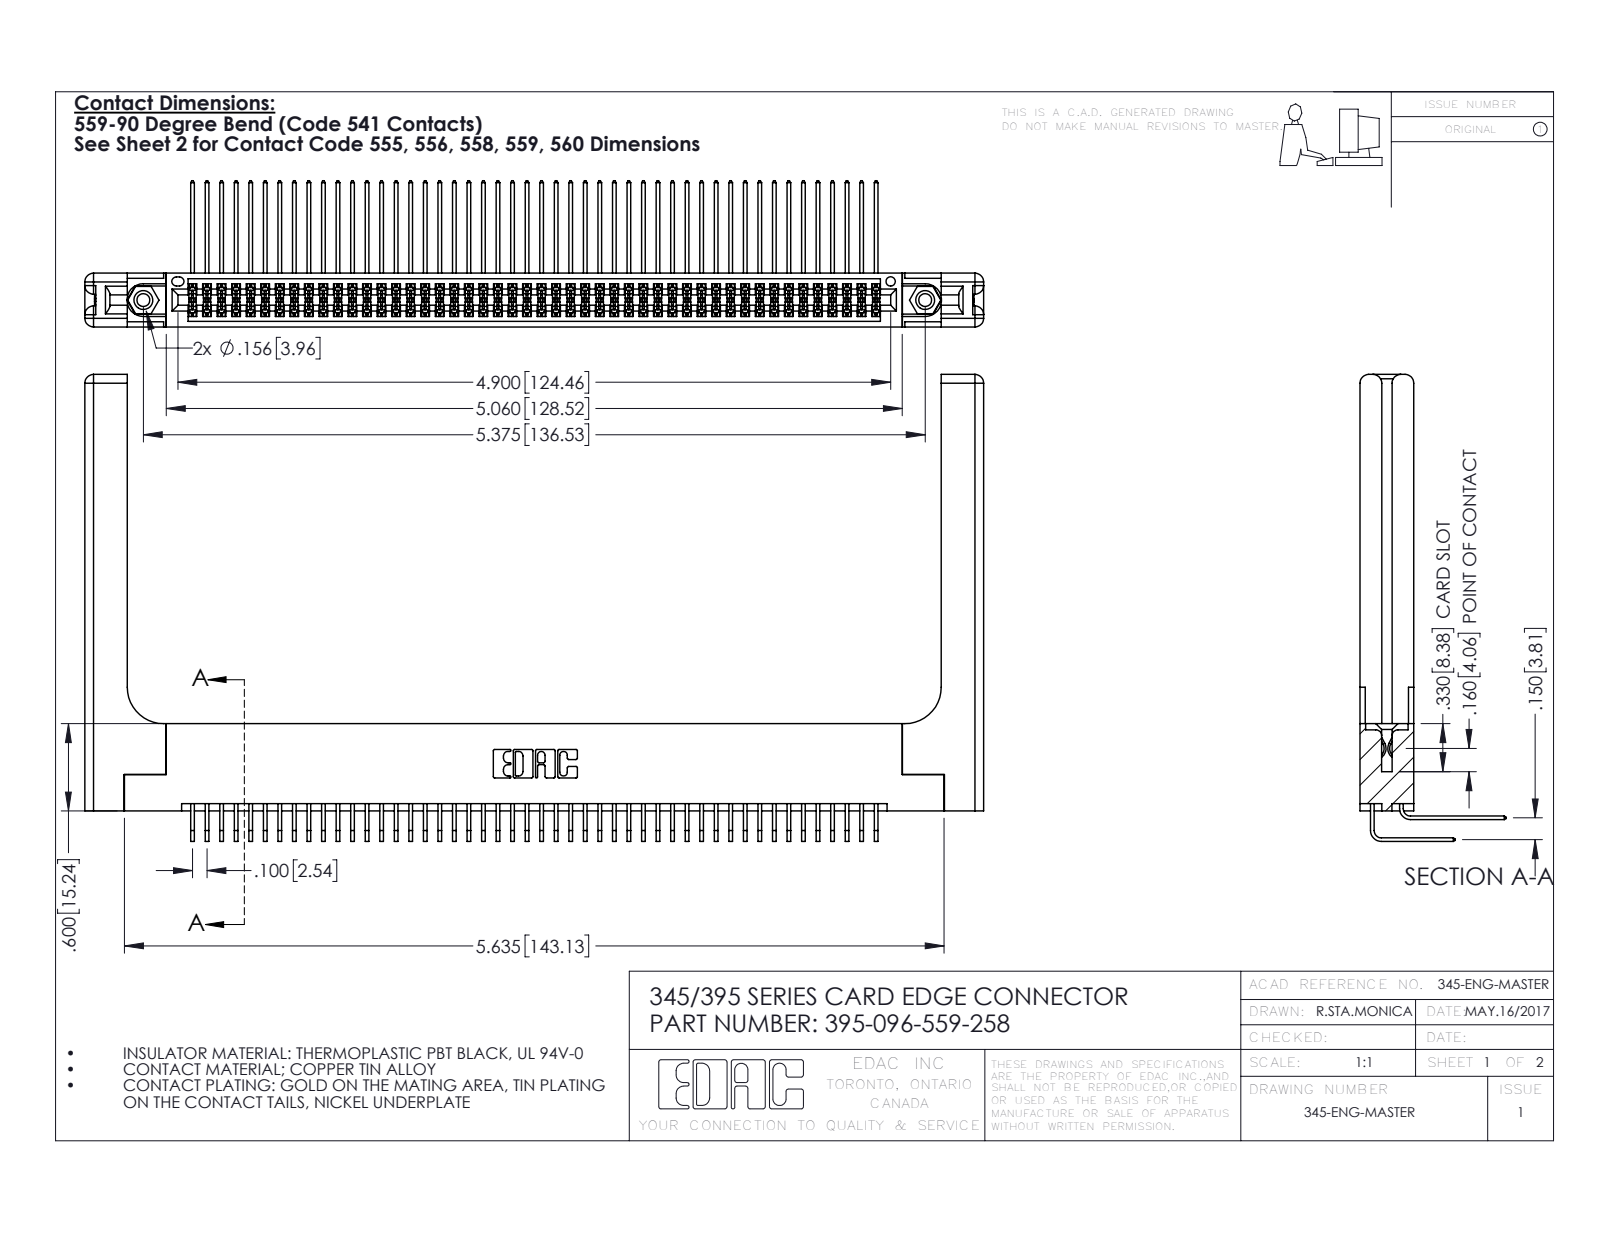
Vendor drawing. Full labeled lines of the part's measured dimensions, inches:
Part name (STEP PRODUCT): 345-250-001_345-250-001-102; 345-292-001_559 Tail - 2; 345-220-058_345-220-058; 395-096-559-258 (+2 more)
STEP written by: SolidWorks 2016 (CONFIG_CONTROL_DESIGN)
Units: inches
Bodies: 101 solids, 5374 faces (3588 planar, 1726 cylindrical, 60 other)
Overall size (bounding box): 6.179 × 3.209 × 1.005
Volume: 1.485 in³ · Surface area: 48.39 in²
Round holes (diameter × count): ⌀0.089 ×2, ⌀0.125 ×2, ⌀0.156 ×2, ⌀0.064 ×1
Round bosses / shafts (diameter × count): ⌀0.155 ×2
Partial cylindrical surfaces — rounded edges, fillets, slot ends (radius × count): R0.006 ×145, R0.01 ×22, R0.06 ×16, R0.007 ×6, R0.031 ×6, R0.026 ×3, R0.014 ×2, R0.019 ×2
Main face-to-face distances: 0.072, 0.298, 0.37, 0.2, 0.098, 0.272, 0.025, 0.225, 0.175, 0.15
Hole centre spacings: 0.27, 5.139, 5.375
